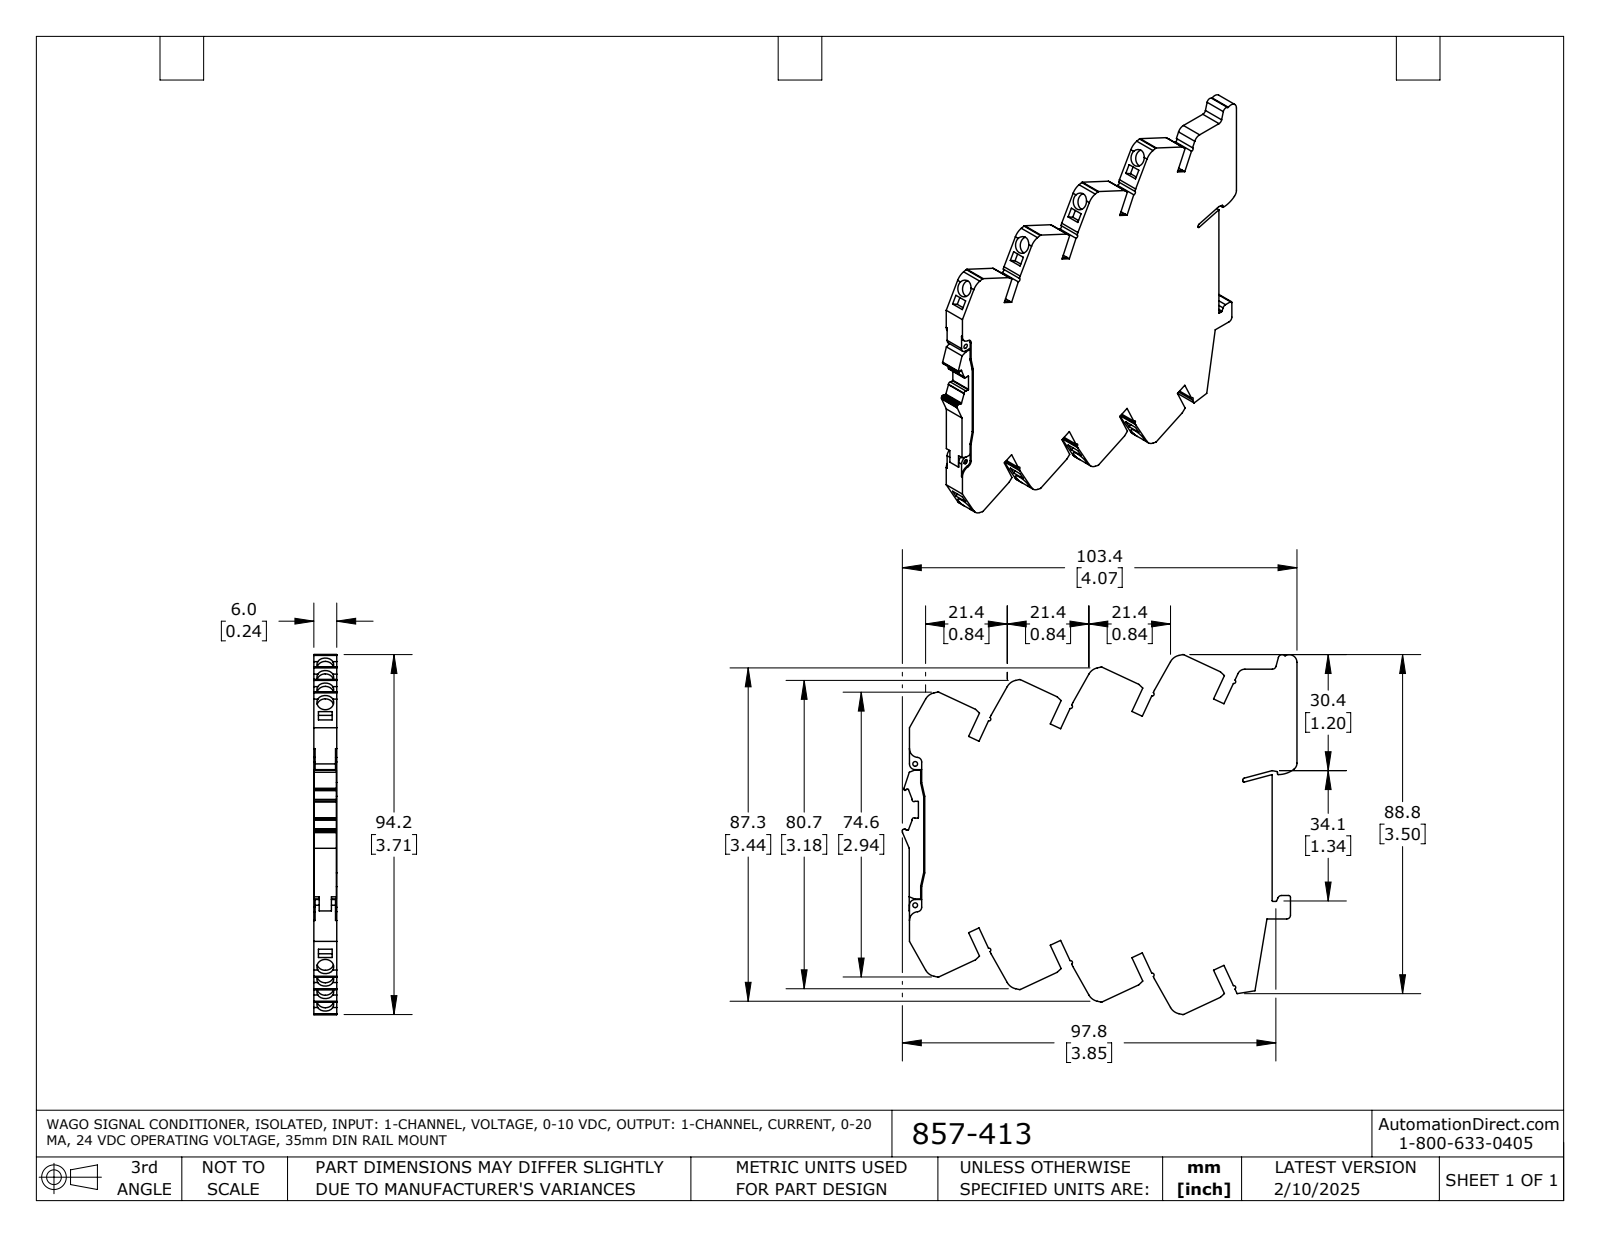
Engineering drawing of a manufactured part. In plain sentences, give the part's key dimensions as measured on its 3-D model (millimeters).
The part is named "857-413". Its 3-D file was written by "SolidWorks 2021 (AUTOMOTIVE_DESIGN)". It is 1 solid with 317 faces: 219 planar, 98 cylindrical and 0 other. Overall it measures 103.4 by 94.3 by 6 millimeters. Its volume is 43 930 cubic millimeters and its surface area 19 260 square millimeters. Round holes: 8 of diameter 4.4, 2 of diameter 1.2. Partial cylindrical surfaces (rounded edges, fillets, slot ends): 12 of radius 0.5, 11 of radius 0.2, 8 of radius 0.4, 8 of radius 3.4, 4 of radius 1, 3 of radius 0.3, 3 of radius 2, 2 of radius 0.5. The main face-to-face distances are 6, 18, 17, 12, 5.9, 12, 3, 24, 36, 6.5. The hole center spacings are 13.4, 13.3, 26.7, 26.7, 26.7, 37, 40, 40.1.
